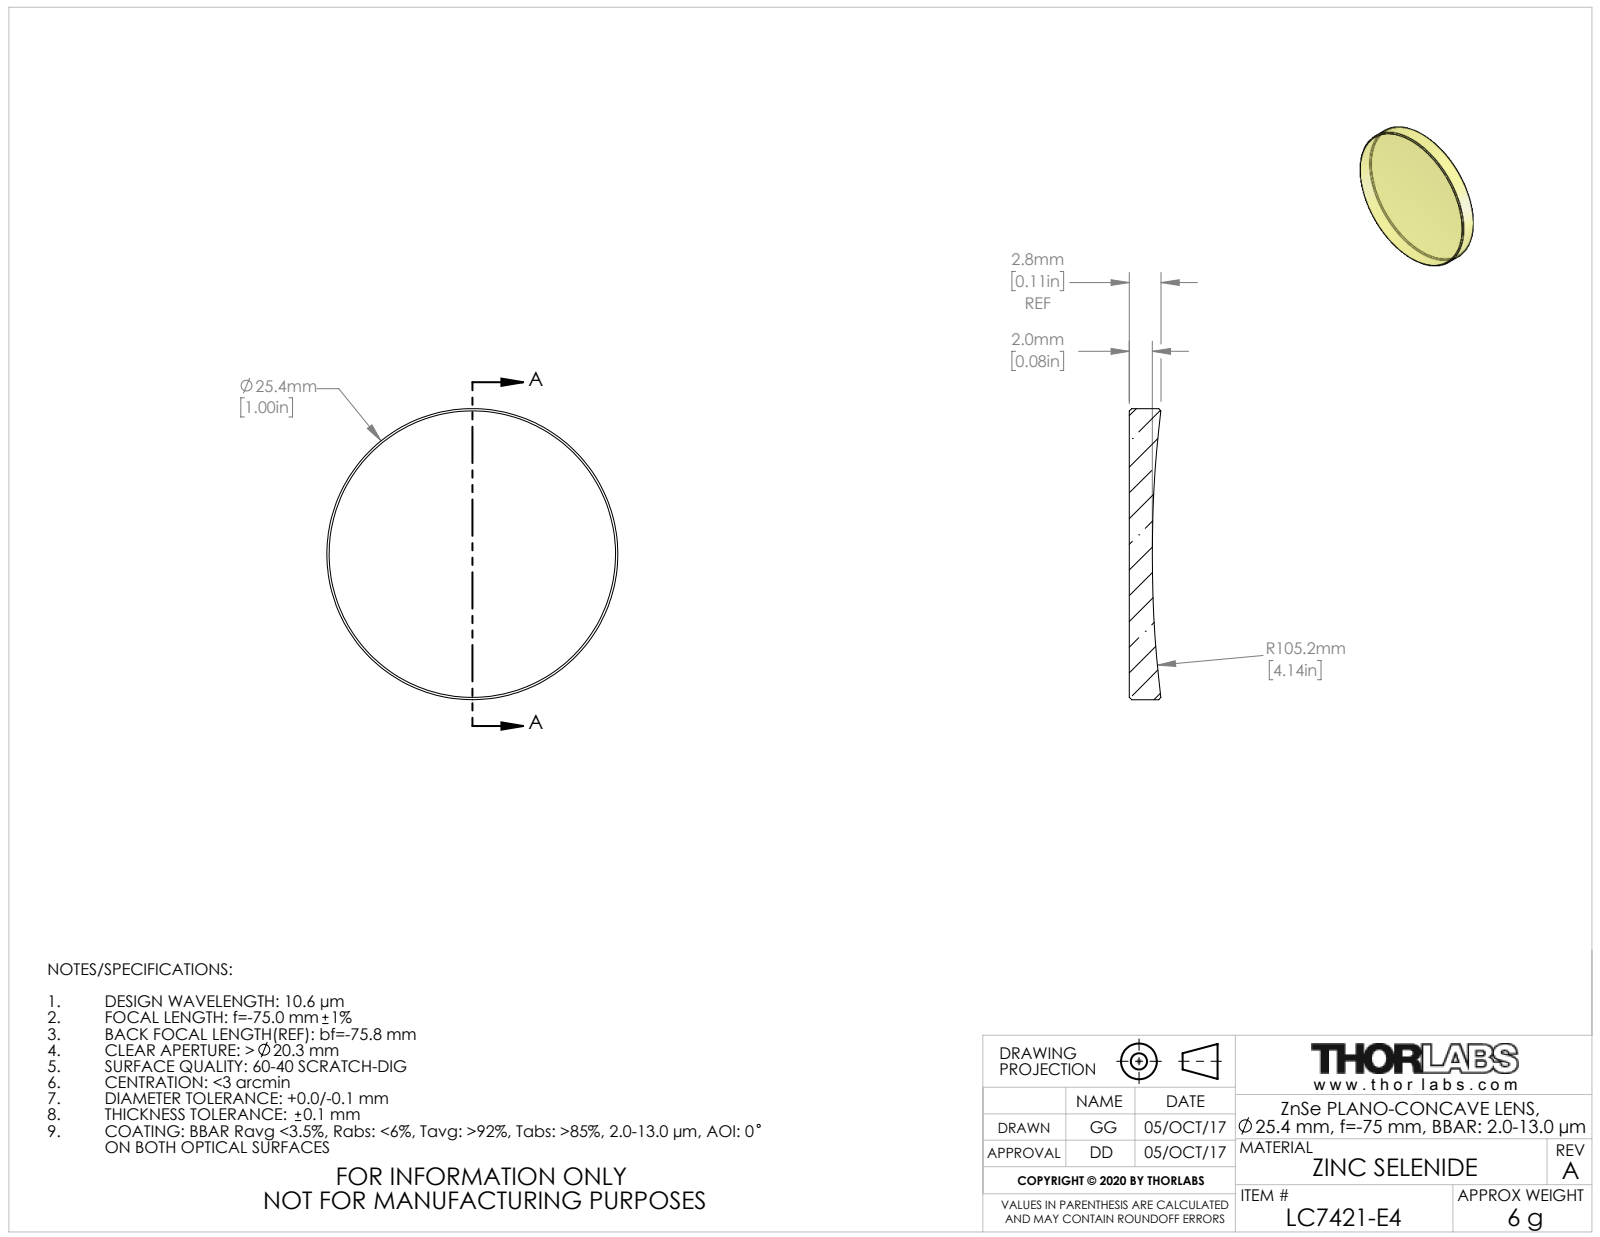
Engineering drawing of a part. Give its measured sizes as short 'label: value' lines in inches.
name: TTN099145-E0W
written by: SolidWorks 2018 (CONFIG_CONTROL_DESIGN)
unit: in
bodies: 1 solid, 9 faces (1 planar, 2 cylindrical, 6 other)
size: 1 × 1 × 0.108
volume: 0.074 in³; area: 1.885 in²
bosses: 1× ⌀1
